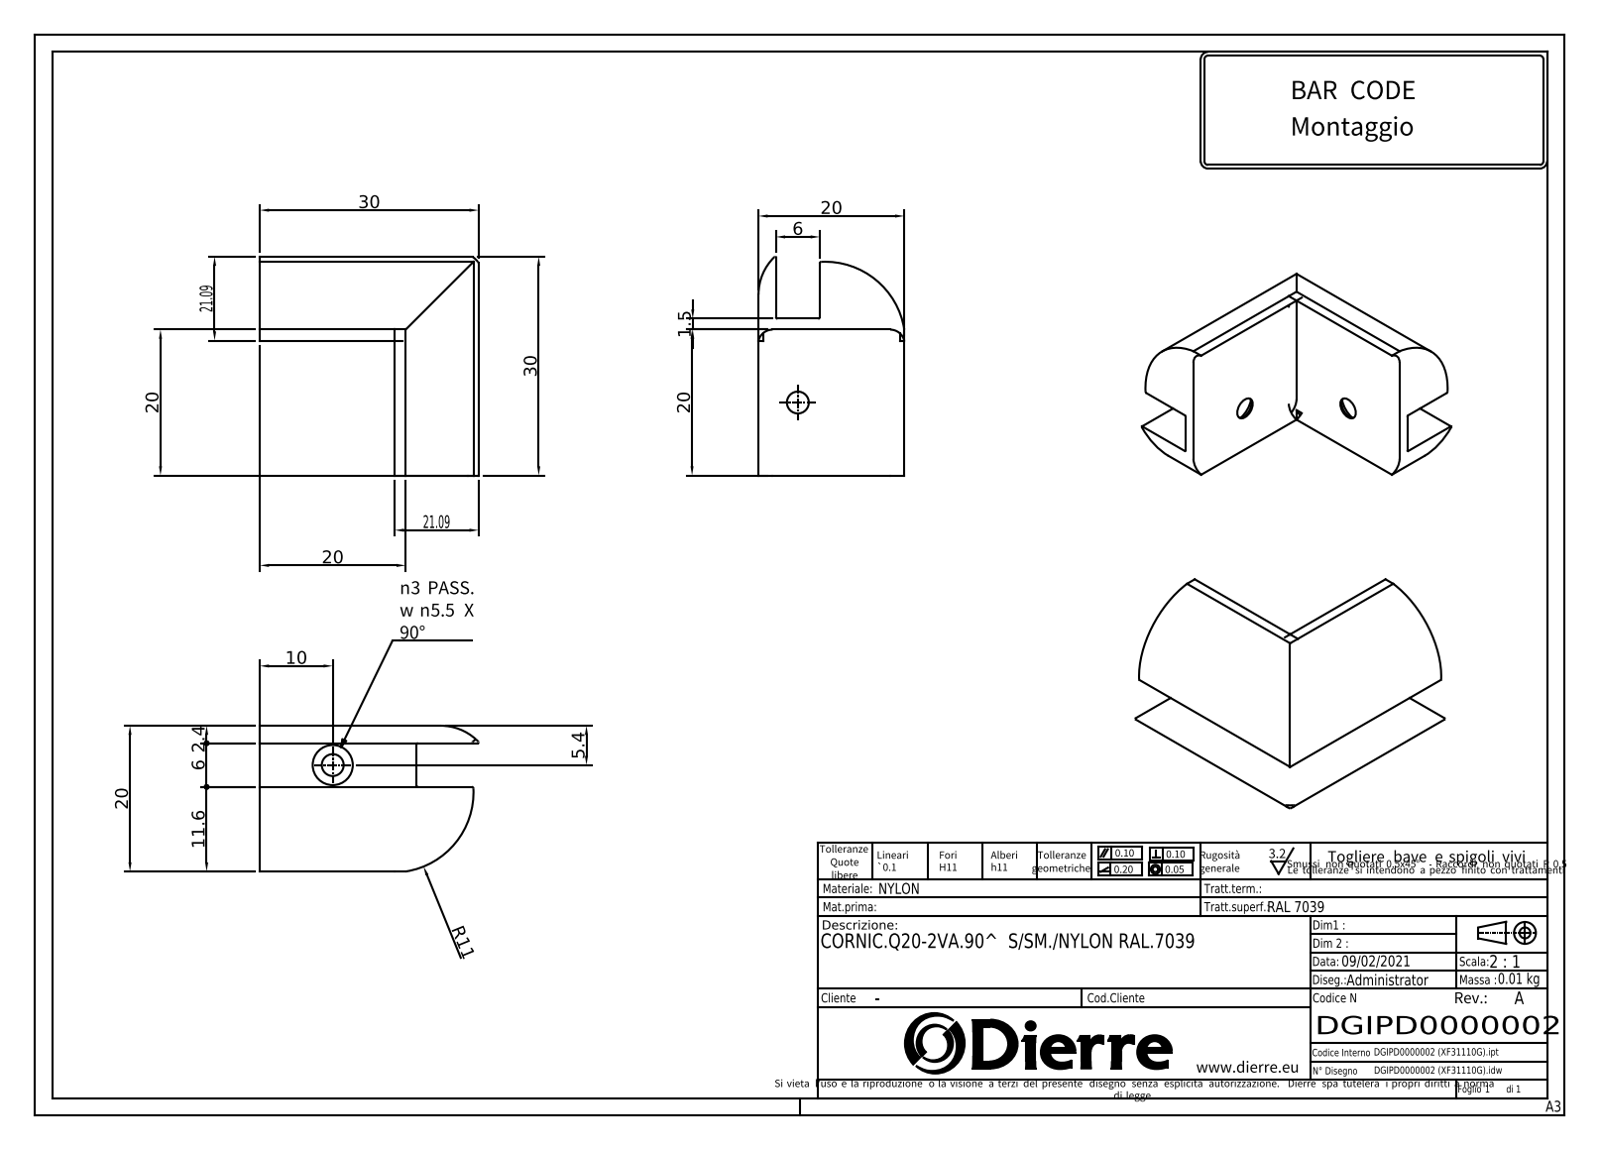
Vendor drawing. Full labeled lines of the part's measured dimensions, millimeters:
Part name (STEP PRODUCT): DGIPD0000002 (XF31110G)
STEP written by: Autodesk Inventor 2019 (AUTOMOTIVE_DESIGN)
Units: millimetres
Bodies: 1 solid, 44 faces (19 planar, 23 cylindrical, 2 other)
Overall size (bounding box): 30 × 30 × 20
Volume: 5 379 mm³ · Surface area: 3 664 mm²
Round holes (diameter × count): ⌀3 ×2
Partial cylindrical surfaces — rounded edges, fillets, slot ends (radius × count): R0.2 ×6, R2 ×4, R7.2 ×2, R11 ×2, R3 ×1
Main face-to-face distances: 6, 20, 2.4, 8.4, 1.5, 21.5, 17.6, 11.6, 30, 10
